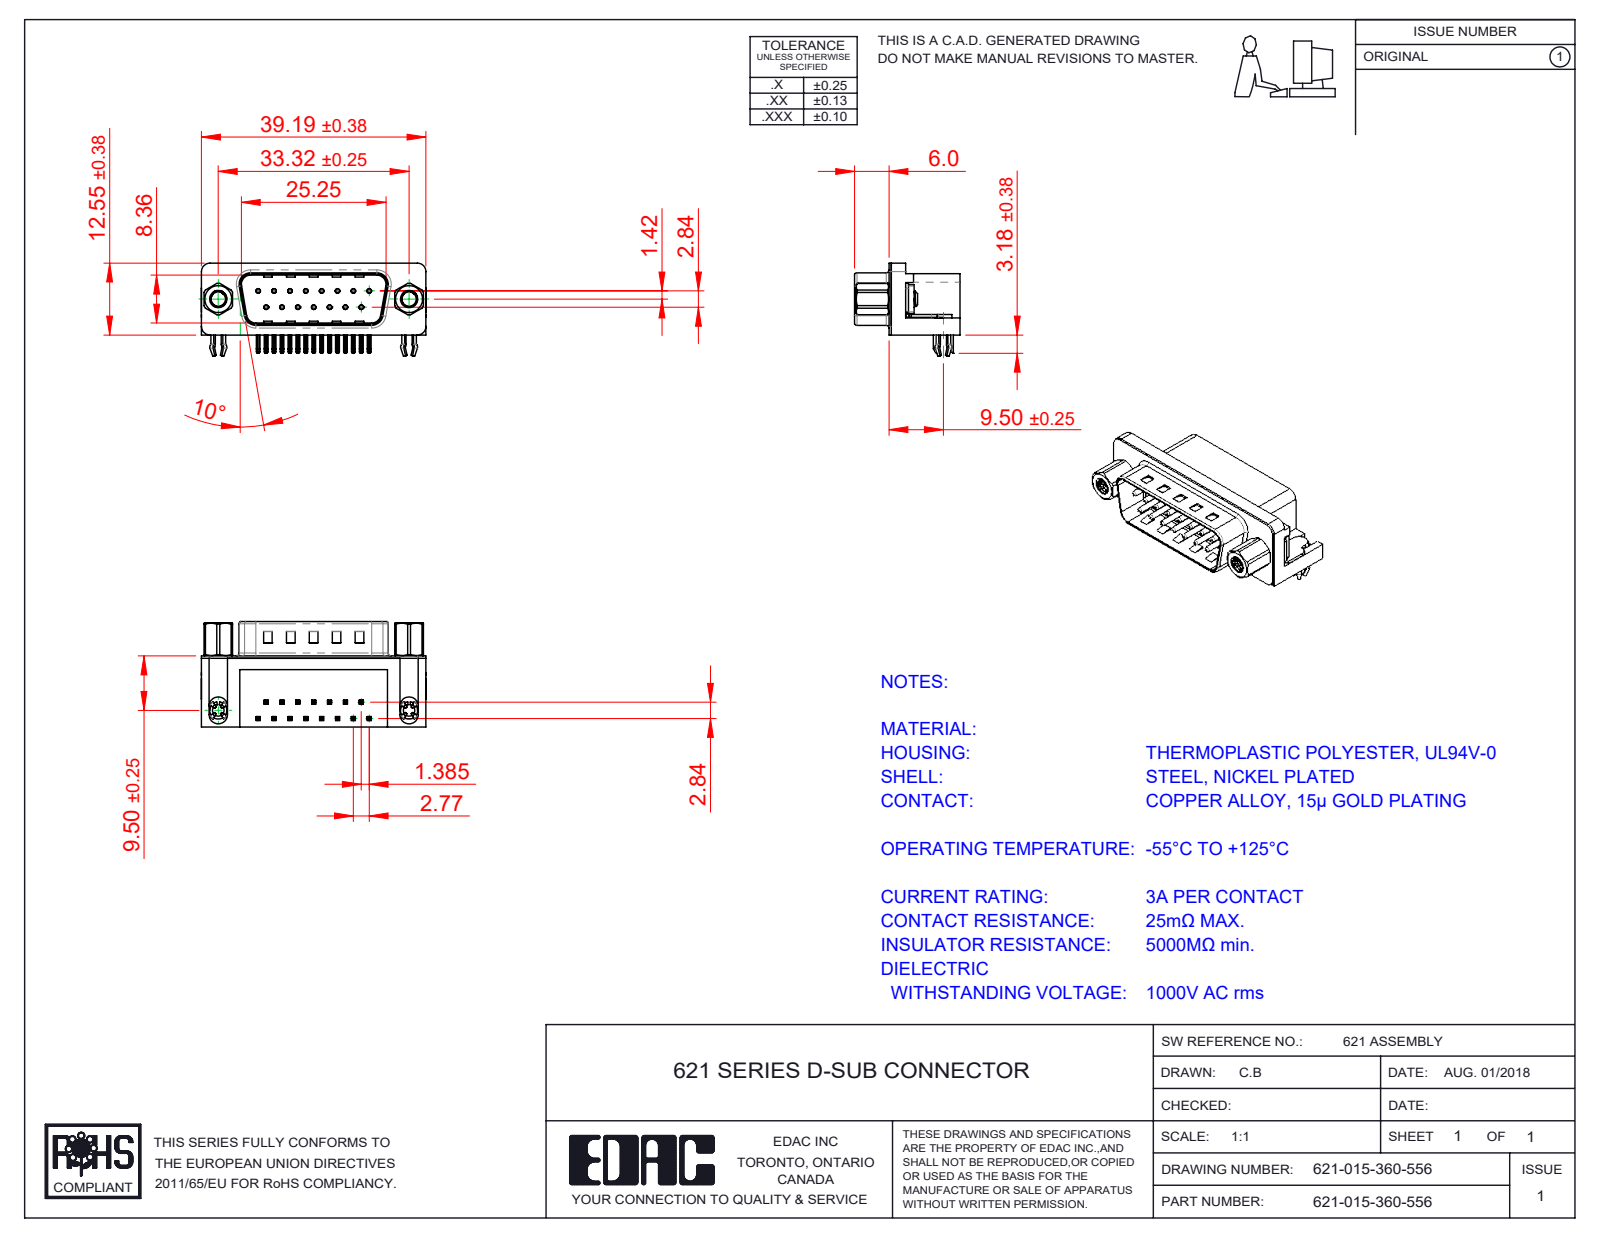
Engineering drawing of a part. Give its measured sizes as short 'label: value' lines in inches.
name: 621 Contact Top; 621 M3 Threaded Rivet; 621 M3 Hex Standoff 5; 621 Contact Bottom (+4 more)
written by: SolidWorks 2016 (CONFIG_CONTROL_DESIGN)
unit: in
bodies: 23 solids, 1655 faces (915 planar, 553 cylindrical, 187 other)
size: 1.544 × 0.724 × 0.619
volume: 0.285 in³; area: 9.706 in²
holes: 15× ⌀0.014, 15× ⌀0.031, 2× ⌀0.089, 2× ⌀0.098, 2× ⌀0.157, 2× ⌀0.189, 2× ⌀0.197
bosses: 15× ⌀0.03, 2× ⌀0.193, 2× ⌀0.187, 2× ⌀0.154, 2× ⌀0.128, 2× ⌀0.118
rounds: 68× R0.01, 30× R0.005, 16× R0.039, 9× R0.02, 8× R0.063, 6× R0.059, 4× R0.035, 4× R0.079
face distances: 0.016, 0.472, 0.407, 0.488, 0.083, 0.412, 0.067, 0.428, 0.345, 0.374
hole spacings: 0.124, 0.109, 0.218, 0.327, 0.436, 0.198, 0.198, 0.294
